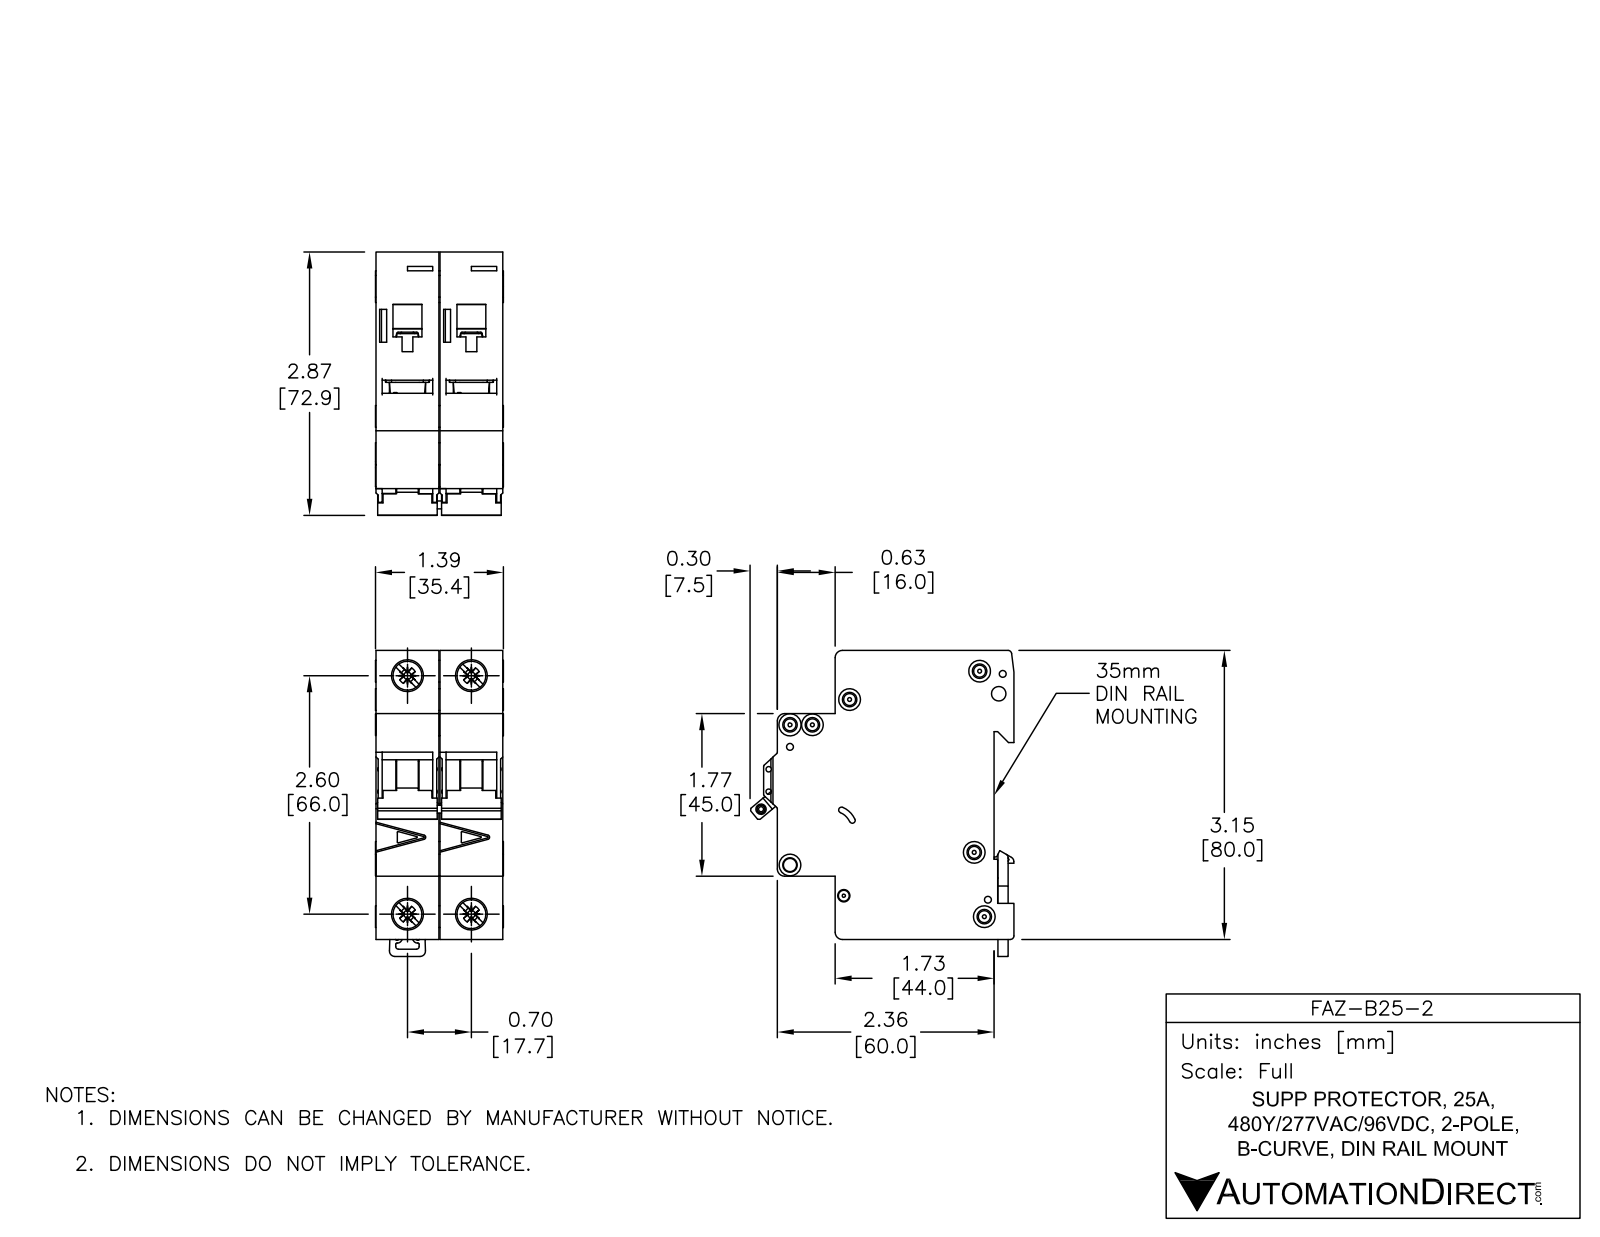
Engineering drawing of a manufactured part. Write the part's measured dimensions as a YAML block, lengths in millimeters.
part_name: "FAZ-B25-2"
step_written_by: "SolidWorks 2014 (AUTOMOTIVE_DESIGN)"
units: millimeters
bodies: {solids: 8, faces: 1104, planar: 466, cylindrical: 396, other: 242}
overall_size: [84.78, 73.04, 35.4]
volume: 149808
surface_area: 38799
round_holes:
  - {diameter: 3.6, count: 6}
  - {diameter: 1.9, count: 3}
  - {diameter: 1.09, count: 2}
  - {diameter: 1.5, count: 2}
  - {diameter: 4, count: 2}
  - {diameter: 7.15, count: 2}
  - {diameter: 8.2, count: 2}
  - {diameter: 2.15, count: 1}
  - {diameter: 2.2, count: 1}
  - {diameter: 2.55, count: 1}
  - {diameter: 3.3, count: 1}
  - {diameter: 3.4, count: 1}
round_bosses_or_shafts:
  - {diameter: 6, count: 4}
  - {diameter: 8.2, count: 2}
  - {diameter: 2.5, count: 2}
partial_cylinders:
  - {radius: 0.25, count: 49}
  - {radius: 0.5, count: 19}
  - {radius: 2, count: 10}
  - {radius: 0.2, count: 8}
  - {radius: 1, count: 8}
  - {radius: 0.8, count: 2}
  - {radius: 1.8, count: 2}
  - {radius: 3, count: 2}
face_to_face_distances: [17.7, 17.5, 35.2, 79.48, 5.5, 49.5, 44, 65.5, 60, 16]
hole_center_spacings: [6.2, 13.64, 17.7, 66, 68.33, 4.81, 5.19, 5.61]
